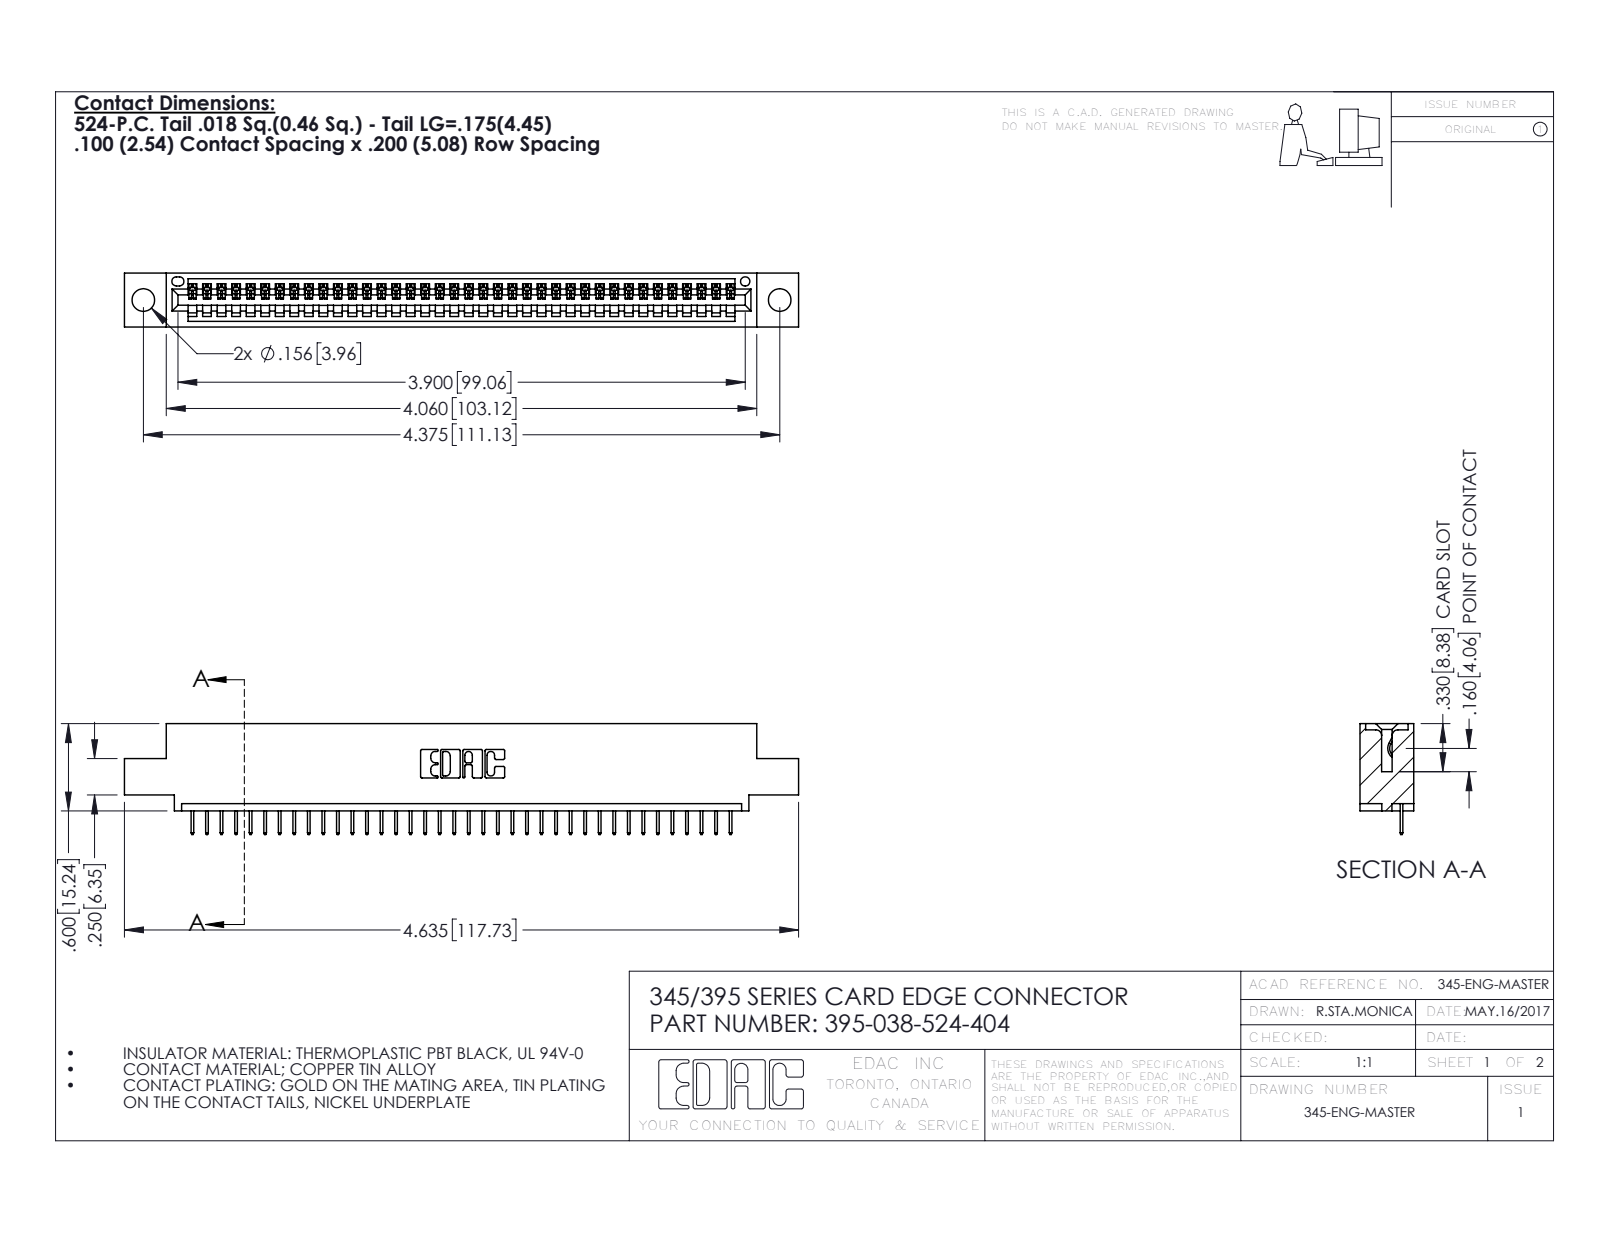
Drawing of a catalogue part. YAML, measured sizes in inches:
part_name: "395-038-524-404; 345 Part_0.110 Offset - 0.156 Dia-TH; 345-292-001_345-293-124"
step_written_by: "SolidWorks 2016 (CONFIG_CONTROL_DESIGN)"
units: inches
bodies: {solids: 39, faces: 2486, planar: 1832, cylindrical: 654, other: 0}
overall_size: [4.635, 0.762, 0.37]
volume: 0.661
surface_area: 21.33
round_holes:
  - {diameter: 0.156, count: 2}
  - {diameter: 0.064, count: 1}
partial_cylinders:
  - {radius: 0.006, count: 76}
  - {radius: 0.01, count: 22}
  - {radius: 0.007, count: 6}
  - {radius: 0.031, count: 6}
  - {radius: 0.026, count: 3}
  - {radius: 0.031, count: 2}
  - {radius: 0.04, count: 2}
  - {radius: 0.014, count: 1}
face_to_face_distances: [0.072, 0.298, 0.37, 0.2, 0.098, 0.272, 0.025, 0.225, 0.072, 0.149]
hole_center_spacings: [0.27, 4.139, 4.375]
